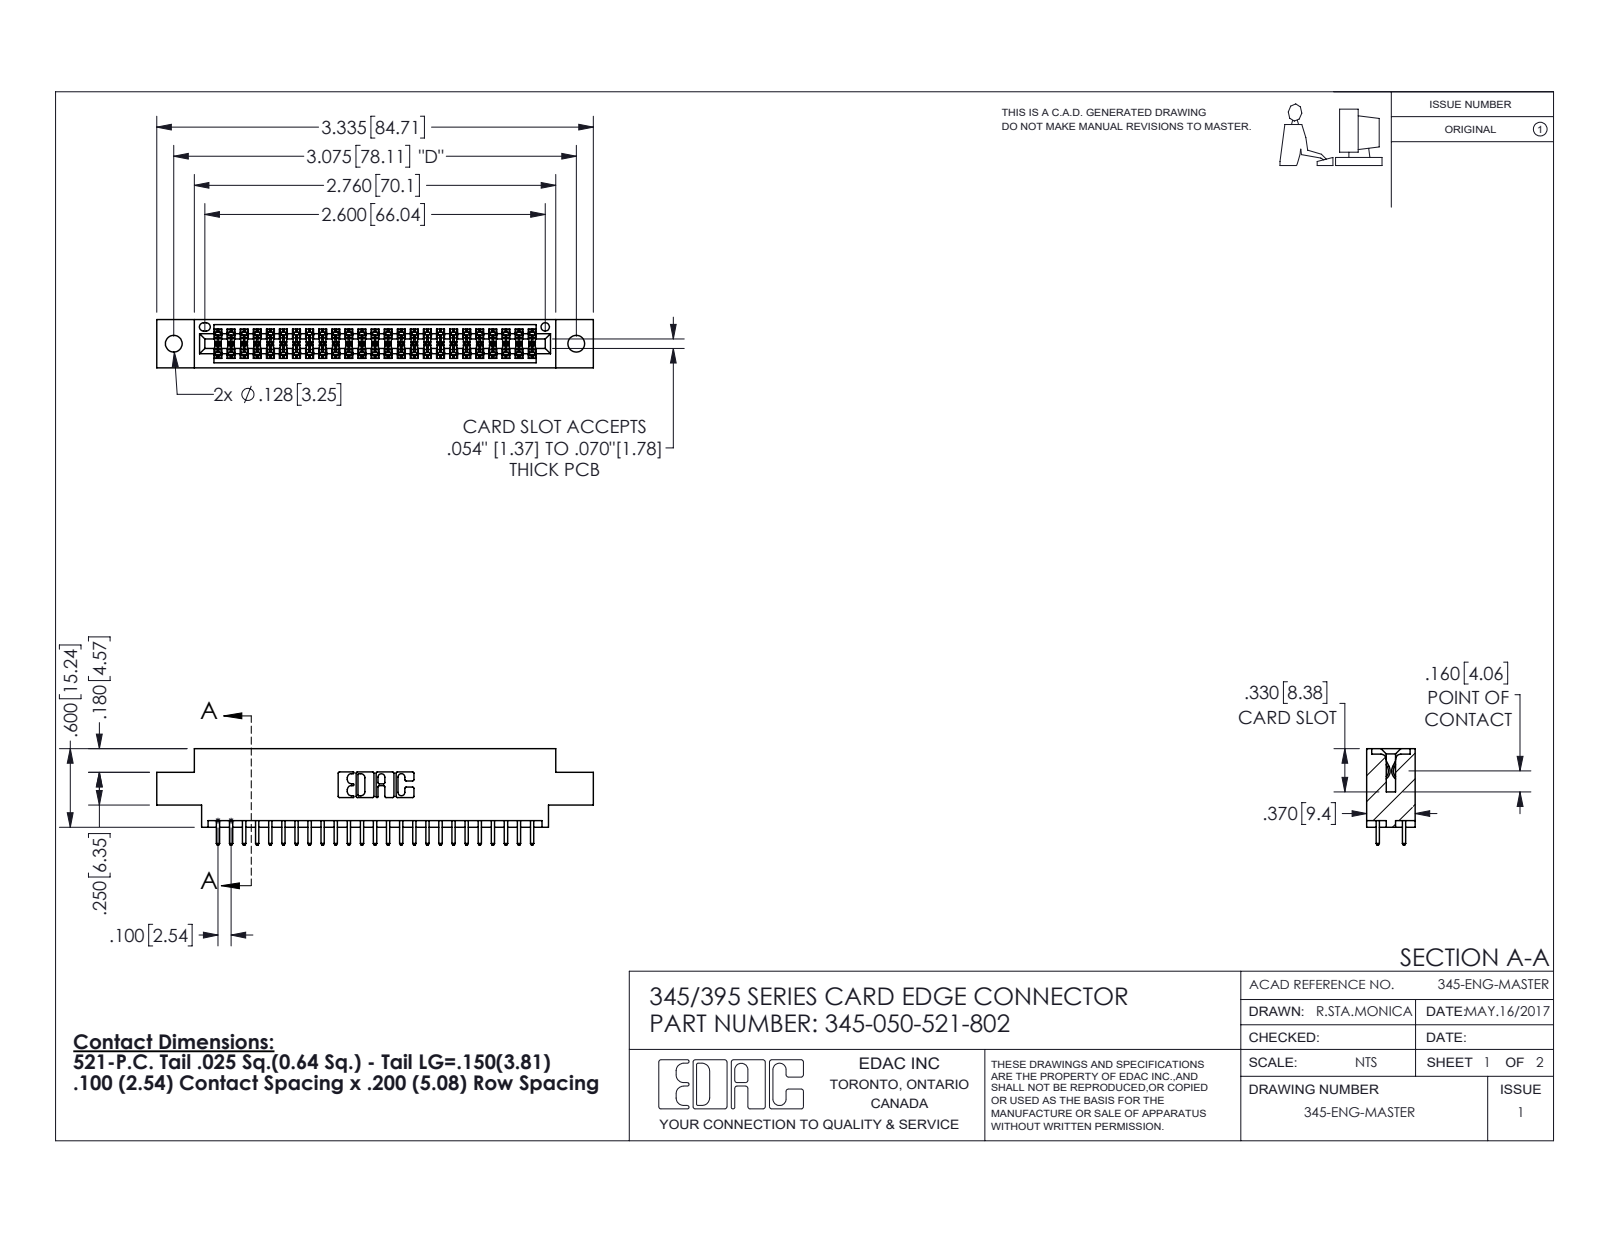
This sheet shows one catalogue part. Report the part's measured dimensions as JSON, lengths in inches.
{"part_name": "345-292-001_345-293-121; 345 Part_0.170 Offset - 0.128 Dia; 345-050-521-802", "step_written_by": "SolidWorks 2016 (CONFIG_CONTROL_DESIGN)", "units": "inches", "bodies": {"solids": 51, "faces": 2630, "planar": 1734, "cylindrical": 896, "other": 0}, "overall_size": [3.335, 0.737, 0.37], "volume_in3": 0.482, "surface_area_in2": 17.18, "round_holes": [[0.128, 2], [0.064, 1]], "partial_cylinders_radius": [[0.006, 75], [0.01, 50], [0.01, 22], [0.007, 6], [0.031, 6], [0.026, 3], [0.014, 2], [0.019, 2]], "face_to_face_distances": [0.298, 0.072, 0.37, 0.2, 0.098, 0.272, 0.025, 0.225, 0.175, 0.149], "hole_center_spacings": [0.27, 2.84, 3.075]}
